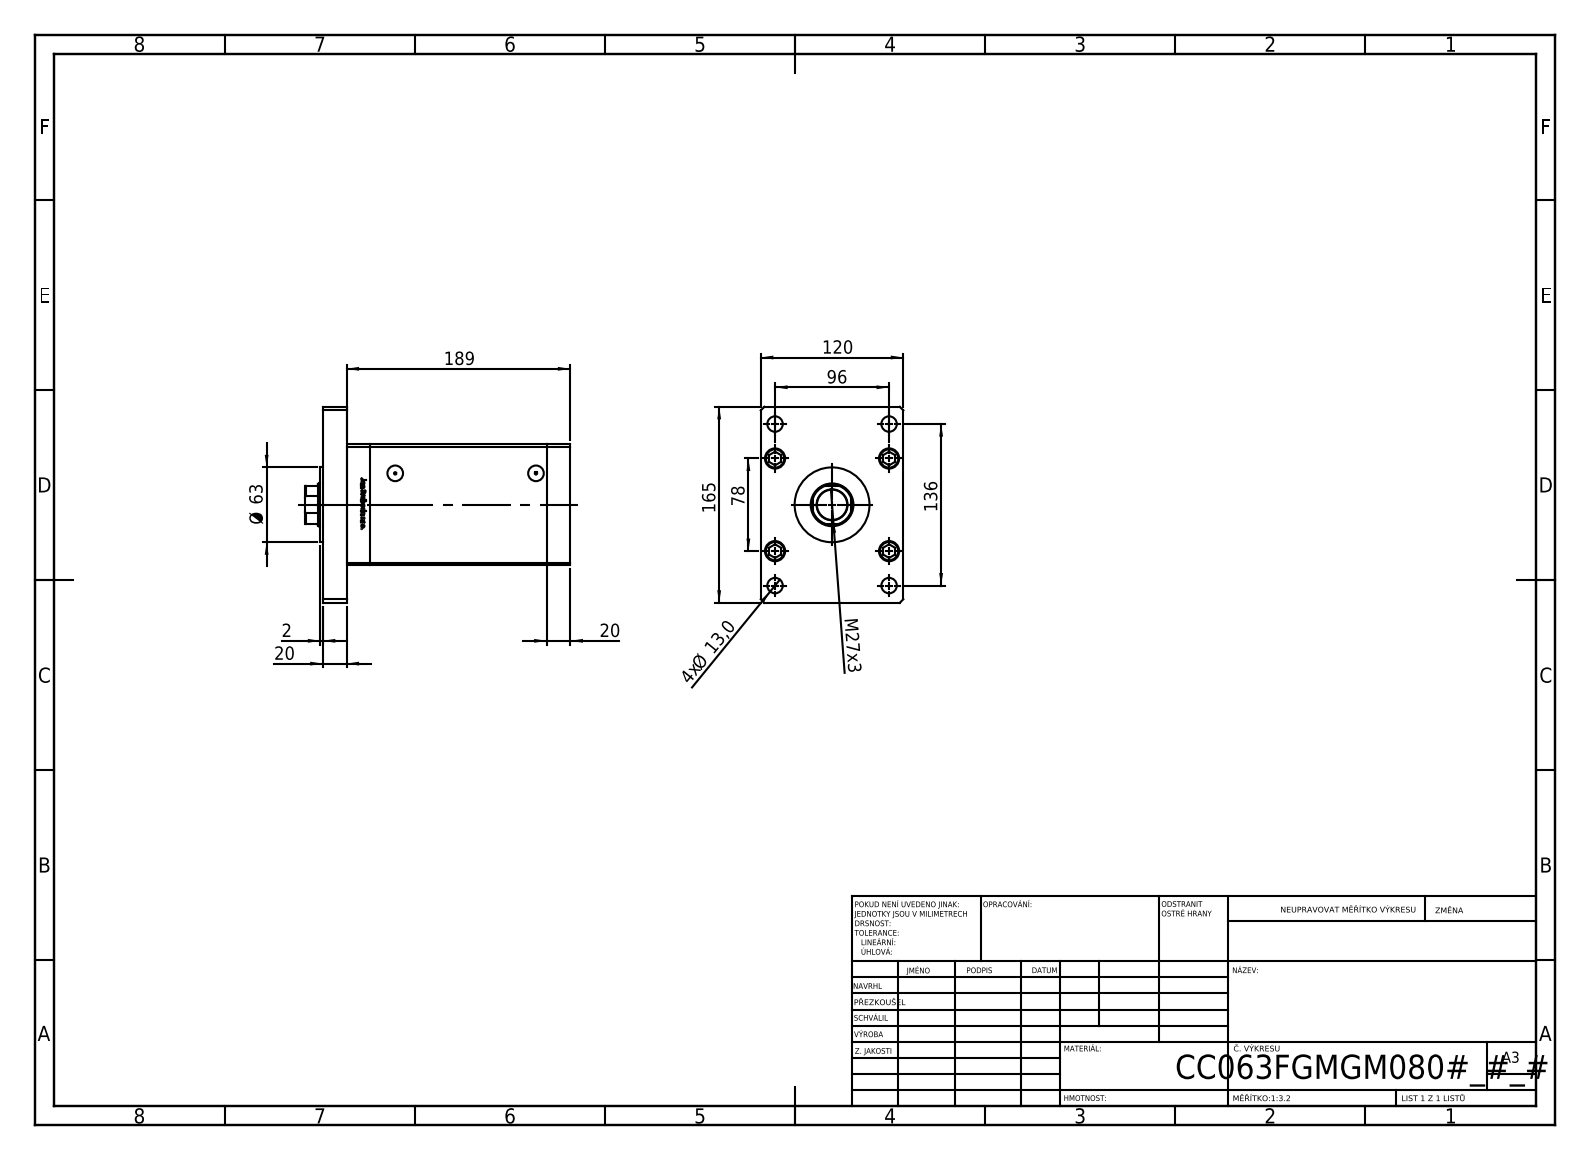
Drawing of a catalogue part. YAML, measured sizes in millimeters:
part_name: "ALLEN BOLT; V220C_VC_F; V220C_F; V220C BACK_F (+2 more)"
step_written_by: "SolidWorks 2019 (CONFIG_CONTROL_DESIGN)"
units: millimeters
bodies: {solids: 19, faces: 1311, planar: 517, cylindrical: 188, other: 606}
overall_size: [223.5, 165, 120]
volume: 2417000
surface_area: 321451
round_holes:
  - {diameter: 13.5, count: 5}
  - {diameter: 18, count: 5}
  - {diameter: 12, count: 4}
  - {diameter: 13, count: 4}
  - {diameter: 17, count: 4}
  - {diameter: 2, count: 2}
  - {diameter: 13.16, count: 2}
  - {diameter: 25.5, count: 1}
  - {diameter: 36, count: 1}
  - {diameter: 37.5, count: 1}
round_bosses_or_shafts:
  - {diameter: 8, count: 9}
  - {diameter: 17, count: 5}
  - {diameter: 63, count: 1}
partial_cylinders:
  - {radius: 0.93, count: 2}
  - {radius: 17.5, count: 1}
face_to_face_distances: [20, 168.5, 188.5, 120, 102, 148.5, 40, 208.5, 34.25, 42]
hole_center_spacings: [41.5, 29, 61.85, 83.23, 96, 100.28, 107, 143.75]
